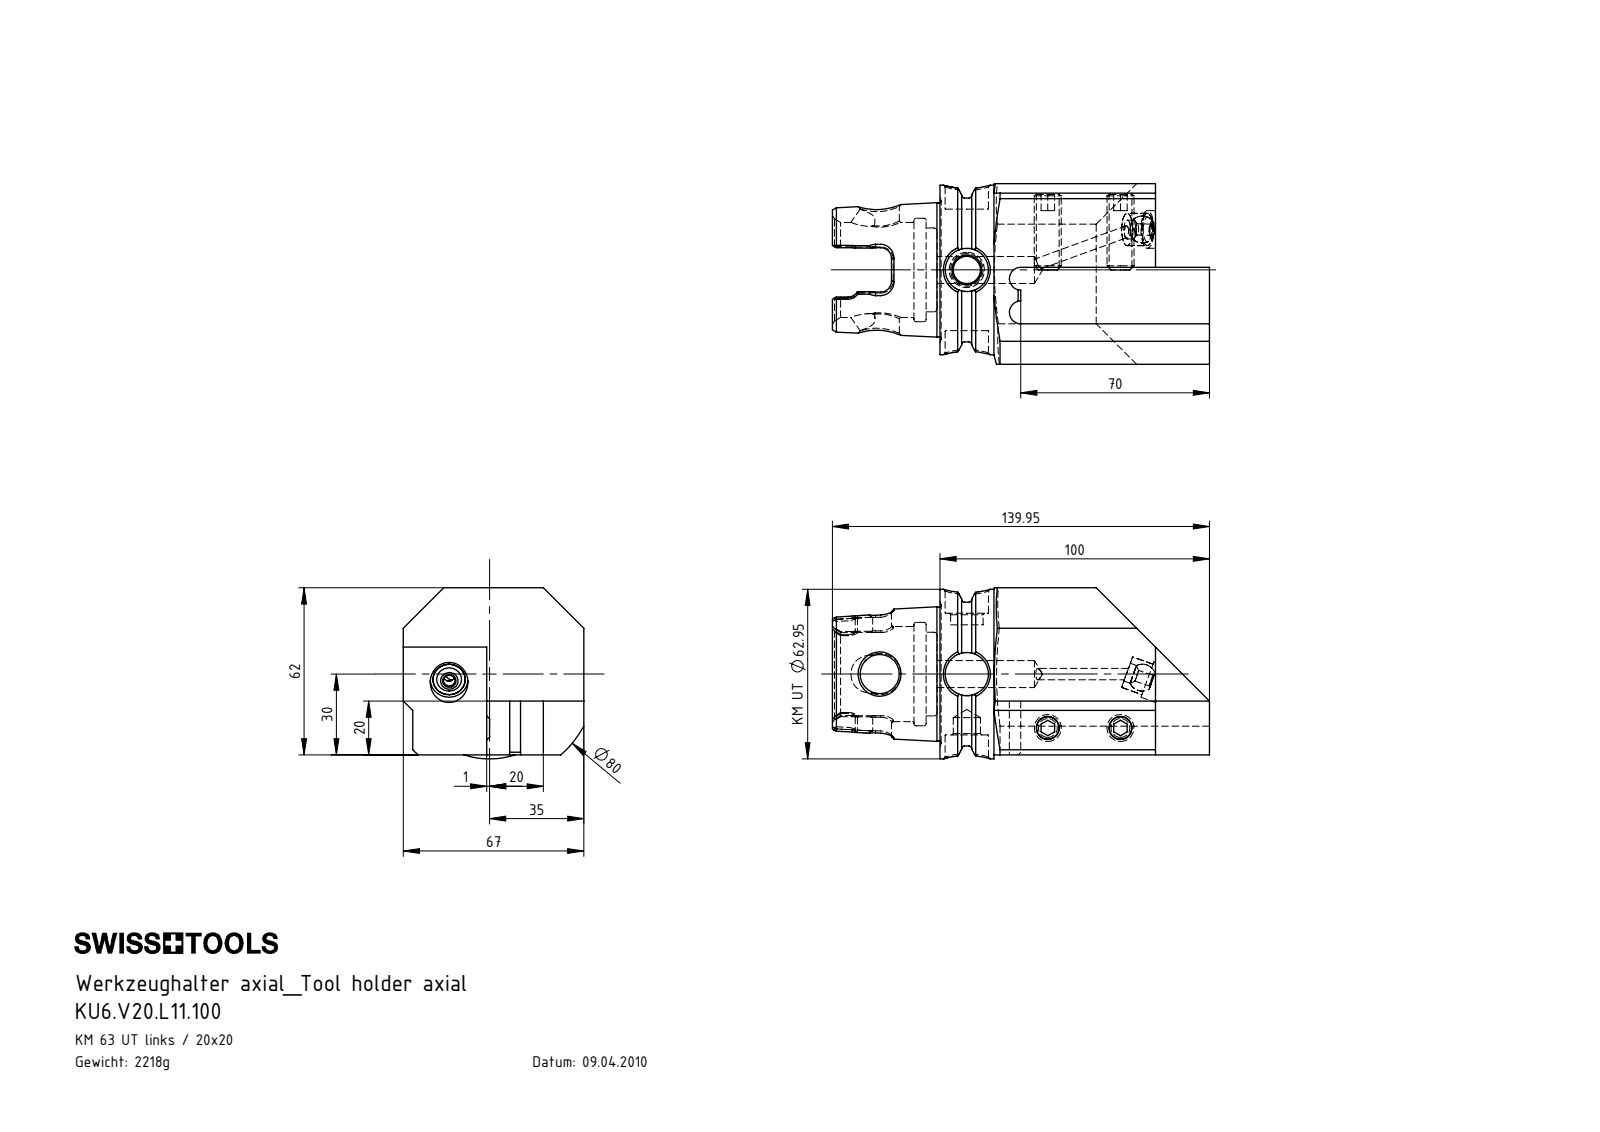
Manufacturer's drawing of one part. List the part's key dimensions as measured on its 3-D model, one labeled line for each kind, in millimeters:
Part name (STEP PRODUCT): KU6-V20.L11.100_A; KU1-U12.001.010_2; ISO 4026 - M10 x 28; KU1-U12.001.010 (+2 more)
STEP written by: SolidWorks 2017 (CONFIG_CONTROL_DESIGN)
Units: millimetres
Bodies: 5 solids, 302 faces (90 planar, 72 cylindrical, 140 other)
Overall size (bounding box): 139.95 × 67 × 63.48
Volume: 282 810 mm³ · Surface area: 46 197 mm²
Round holes (diameter × count): ⌀4.2 ×2, ⌀8.5 ×2, ⌀16.05 ×2, ⌀7 ×1, ⌀10 ×1, ⌀10.1 ×1, ⌀12 ×1, ⌀12.1 ×1, ⌀14 ×1, ⌀14.5 ×1, ⌀31.1 ×1, ⌀35.27 ×1
Round bosses / shafts (diameter × count): ⌀10 ×2, ⌀62.95 ×1, ⌀12 ×1
Partial cylindrical surfaces — rounded edges, fillets, slot ends (radius × count): R4 ×6, R4.25 ×2, R7.04 ×2, R27.85 ×1, R40 ×1
Main face-to-face distances: 20, 67, 42, 15, 52, 62, 21, 36, 31, 80
Hole centre spacings: 27, 32.35, 36.1, 60.45, 65.53, 91.61
